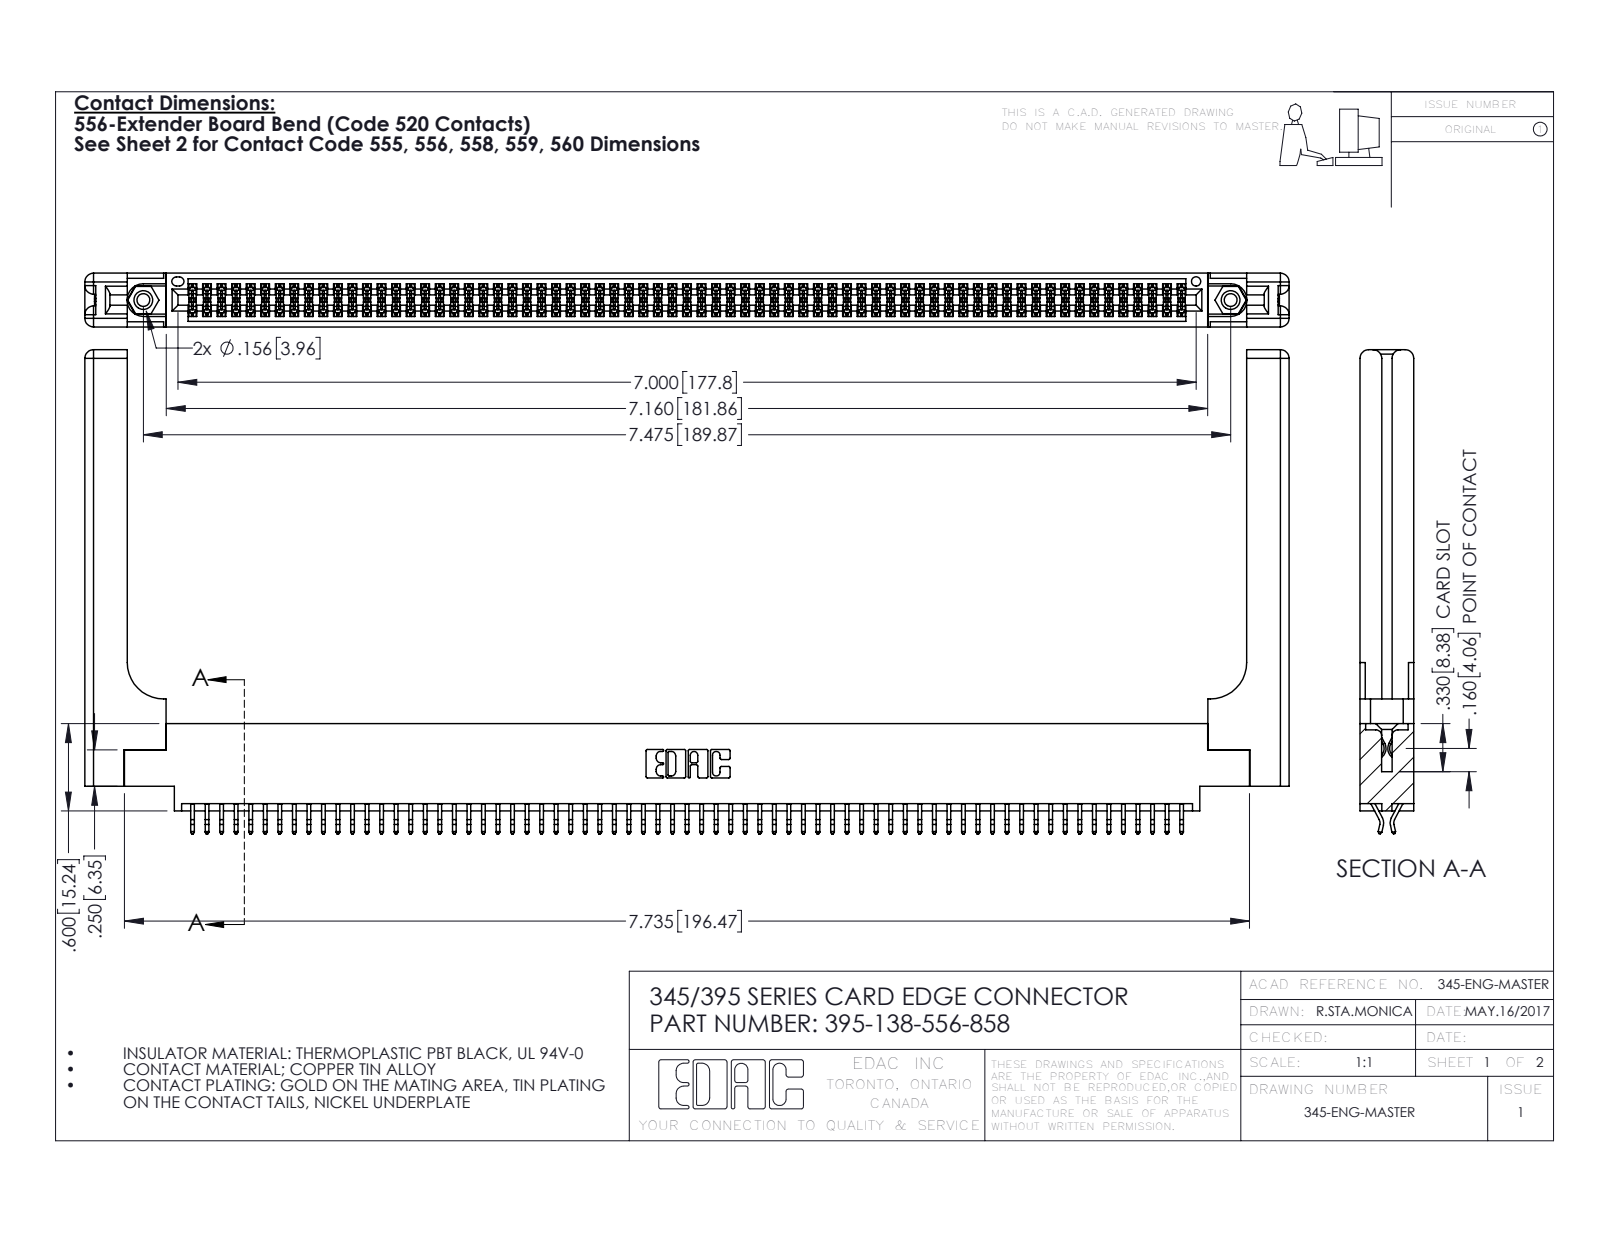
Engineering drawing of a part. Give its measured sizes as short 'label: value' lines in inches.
name: 345-220-058_345-220-058; 395-138-556-858; 345-250-001_345-250-001-102; 345 Part_0.170 Offset - 0.156 Dia-TH (+1 more)
written by: SolidWorks 2016 (CONFIG_CONTROL_DESIGN)
unit: in
bodies: 143 solids, 8114 faces (5338 planar, 2716 cylindrical, 60 other)
size: 8.279 × 3.327 × 0.37
volume: 1.772 in³; area: 55.79 in²
holes: 2× ⌀0.089, 2× ⌀0.125, 2× ⌀0.156, 1× ⌀0.064
bosses: 2× ⌀0.155
rounds: 207× R0.006, 22× R0.01, 16× R0.06, 6× R0.007, 6× R0.031, 3× R0.026, 2× R0.01, 2× R0.014
face distances: 0.072, 0.298, 0.37, 0.025, 0.098, 0.272, 0.2, 0.225, 0.175, 0.148
hole spacings: 0.27, 7.239, 7.475
